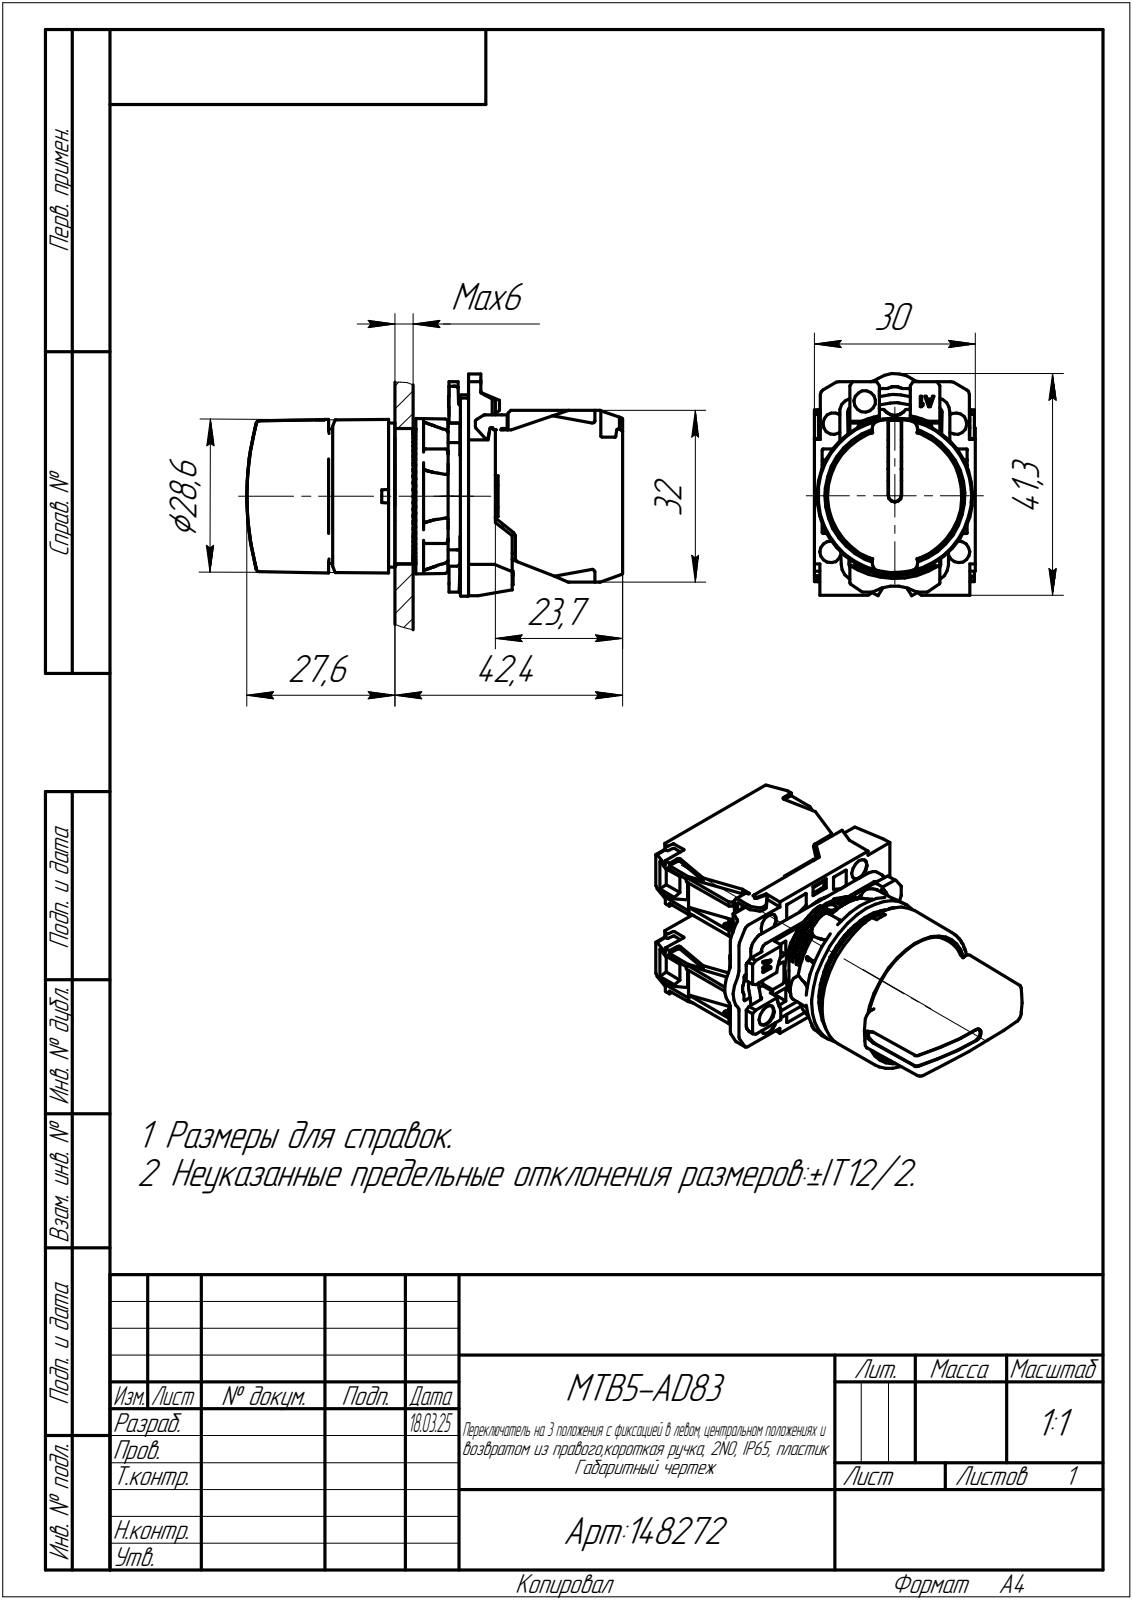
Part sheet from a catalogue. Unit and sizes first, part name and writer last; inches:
Units: inches
Overall size (bounding box): 2.756 × 1.631 × 1.181
Round holes (diameter × count): ⌀0.047 ×7, ⌀0.157 ×5, ⌀0.098 ×4, ⌀0.102 ×4, ⌀0.039 ×2, ⌀0.079 ×1, ⌀0.118 ×1, ⌀0.882 ×1, ⌀0.917 ×1
Round bosses / shafts (diameter × count): ⌀0.22 ×4, ⌀0.114 ×4, ⌀0.094 ×4, ⌀1 ×1, ⌀0.984 ×1, ⌀0.827 ×1, ⌀0.787 ×1, ⌀0.013 ×1
Partial cylindrical surfaces — rounded edges, fillets, slot ends (radius × count): R0.008 ×176, R0.004 ×126, R0.02 ×41, R0.012 ×38, R0.039 ×33, R0.006 ×18, R0.016 ×14, R0.079 ×14
Main face-to-face distances: 0.787, 0.386, 0.039, 0.197, 0.059, 1.173, 0.38, 0.051, 0.252, 0.063
Hole centre spacings: 0.177, 0.293, 0.343, 0.485, 0.625, 0.694, 0.787, 0.935
Volume: 1.841 in³ · Surface area: 38.54 in²
Bodies: 24 solids, 5276 faces (3092 planar, 1282 cylindrical, 902 other)
Part name (STEP PRODUCT): ZB5AZ009; ZBE101; ZB5AD3C; XB5AD33_ASM
STEP written by: PRO/ENGINEER BY PARAMETRIC TECHNOLOGY CORPORATION, 2010280 (AUTOMOTIVE_DESIGN)
